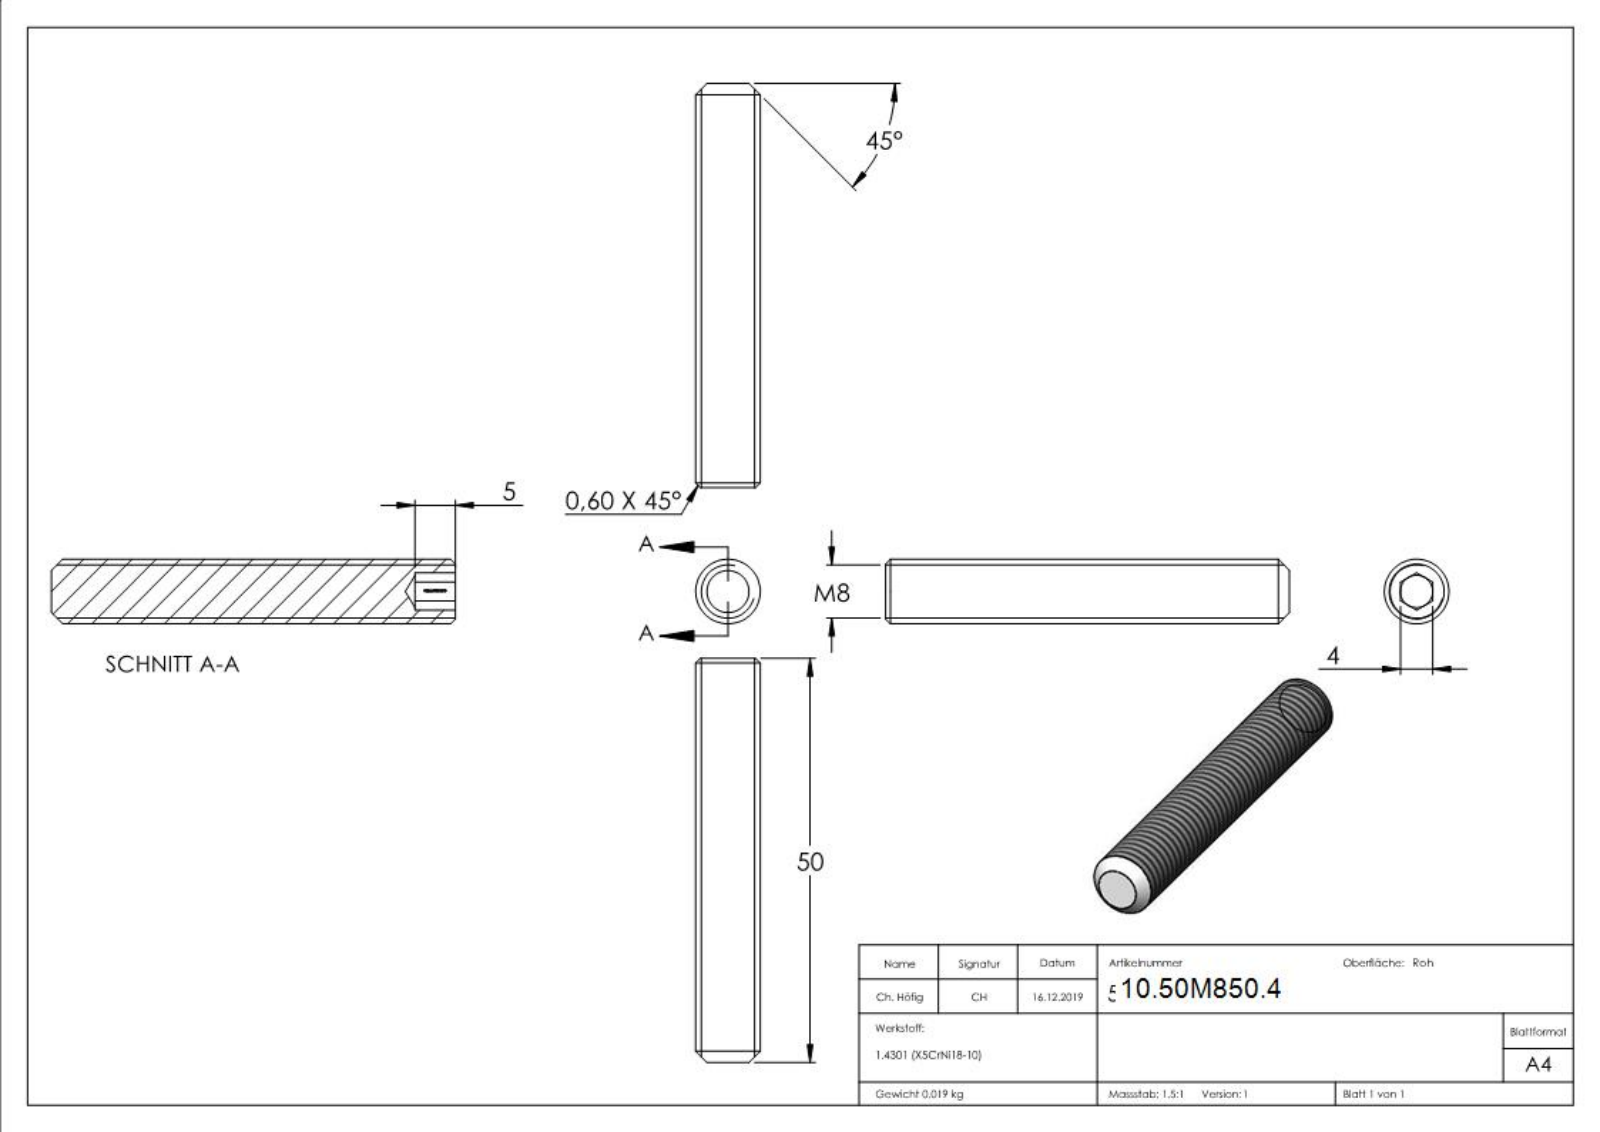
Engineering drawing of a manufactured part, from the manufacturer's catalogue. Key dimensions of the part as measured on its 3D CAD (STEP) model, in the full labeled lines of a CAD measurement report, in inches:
Part name (STEP PRODUCT): 58300-240-50
STEP written by: SolidWorks 2015 (CONFIG_CONTROL_DESIGN)
Units: inches
Bodies: 1 solid, 296 faces (140 planar, 1 cylindrical, 155 other)
Overall size (bounding box): 2.756 × 0.315 × 0.315
Volume: 0.147 in³ · Surface area: 2.167 in²
Round bosses / shafts (diameter × count): ⌀0.315 ×1
Main face-to-face distances: 0.157, 1.969, 1.772, 0.197, 0.161, 0.019, 0.021, 0.066, 0.012, 0.063
